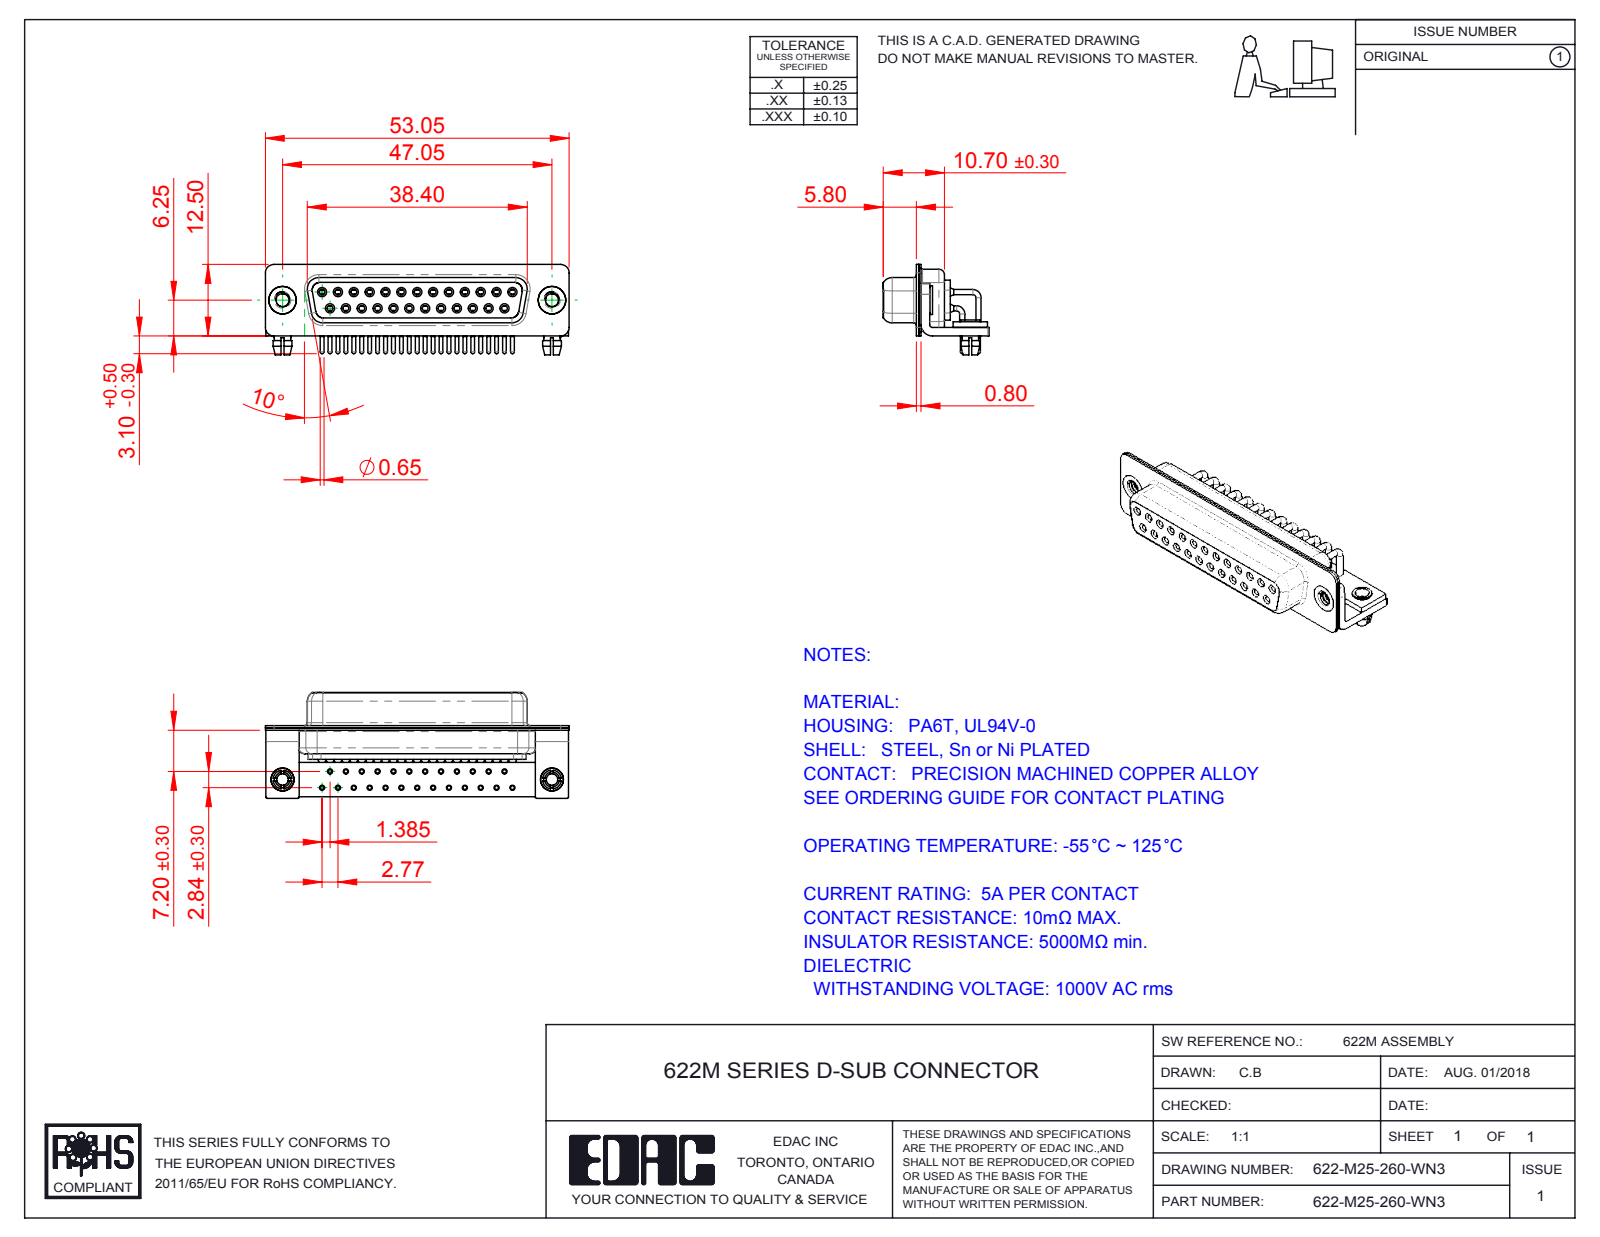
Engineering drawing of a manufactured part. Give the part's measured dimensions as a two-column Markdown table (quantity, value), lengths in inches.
| quantity | value |
| --- | --- |
| part name | 622M Stabilizer Bracket; 622M 4-40 Threaded Rivet_Stabilizer; 622M Contact Row 2; 622M Contact Row 1 (+6 more) |
| STEP written by | SolidWorks 2016 (CONFIG_CONTROL_DESIGN) |
| units | inches |
| bodies | 35 solids, 1796 faces (516 planar, 816 cylindrical, 464 other) |
| overall size | 2.089 × 0.728 × 0.622 |
| volume | 0.269 in³ |
| surface area | 17.12 in² |
| round holes (diameter × count) | 0.079 × 27, 0.035 × 25, 0.039 × 25, 0.043 × 25, 0.067 × 25, 0.071 × 25, 0.089 × 2, 0.098 × 2, 0.126 × 2, 0.157 × 2, 0.189 × 2 |
| round bosses / shafts (diameter × count) | 0.035 × 27, 0.063 × 25, 0.059 × 25, 0.026 × 25, 0.197 × 2, 0.193 × 2, 0.157 × 2, 0.134 × 2 |
| partial cylindrical surfaces (radius × count) | 0.01 × 16, 0.059 × 16, 0.079 × 13, 0.053 × 8, 0.063 × 8, 0.02 × 5, 0.024 × 4, 0.026 × 4 |
| main face-to-face distances | 0.016, 0.091, 0.075, 0.057, 0.352, 0.033, 0.031, 0.244, 0.368, 0.039 |
| hole center spacings | 0.124, 0.109, 0.218, 0.327, 0.436, 0.545, 0.654, 0.198 |
